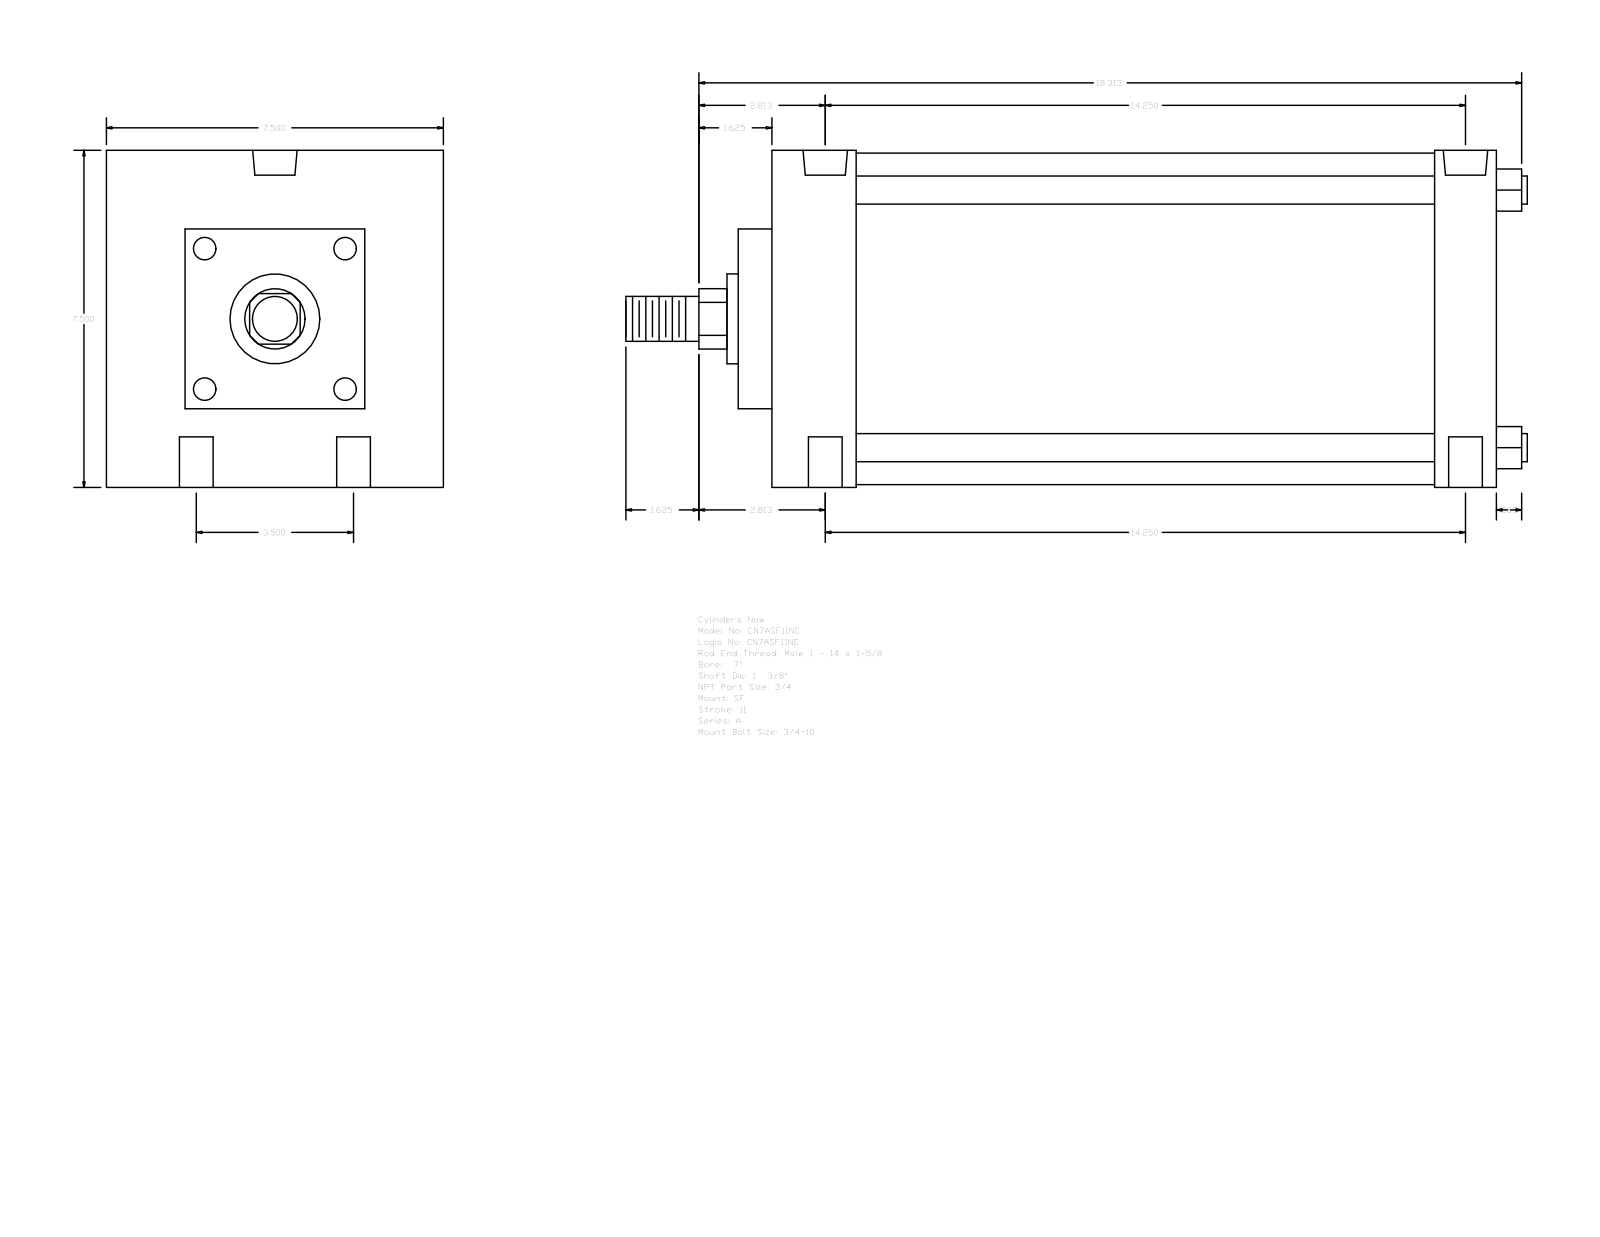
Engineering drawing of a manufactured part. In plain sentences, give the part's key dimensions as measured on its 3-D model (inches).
The part is named "A_SF__0700_1.375". Its 3-D file was written by "GSSL Pune (CONFIG_CONTROL_DESIGN)". It is 0 solids with 93 faces: 67 planar, 26 cylindrical and 0 other. Overall it measures 20.063 by 7.5 by 7.5 inches. Round holes: 4 of diameter 0.75, 2 of diameter 0.594, 2 of diameter 0.989. Round bosses or shafts: 4 of diameter 0.625, 1 of diameter 7.375, 1 of diameter 2, 1 of diameter 1.375, 1 of diameter 1. Partial cylindrical surfaces (rounded edges, fillets, slot ends): 1 of radius 0.672. The main face-to-face distances are 7.5, 16.125, 0.75, 16.875, 2.625, 15.5, 1.875, 14.75, 12.875, 14.25. The hole center spacings are 1.75, 14.357, 14.25, 3.5, 14.674, 13.812.
